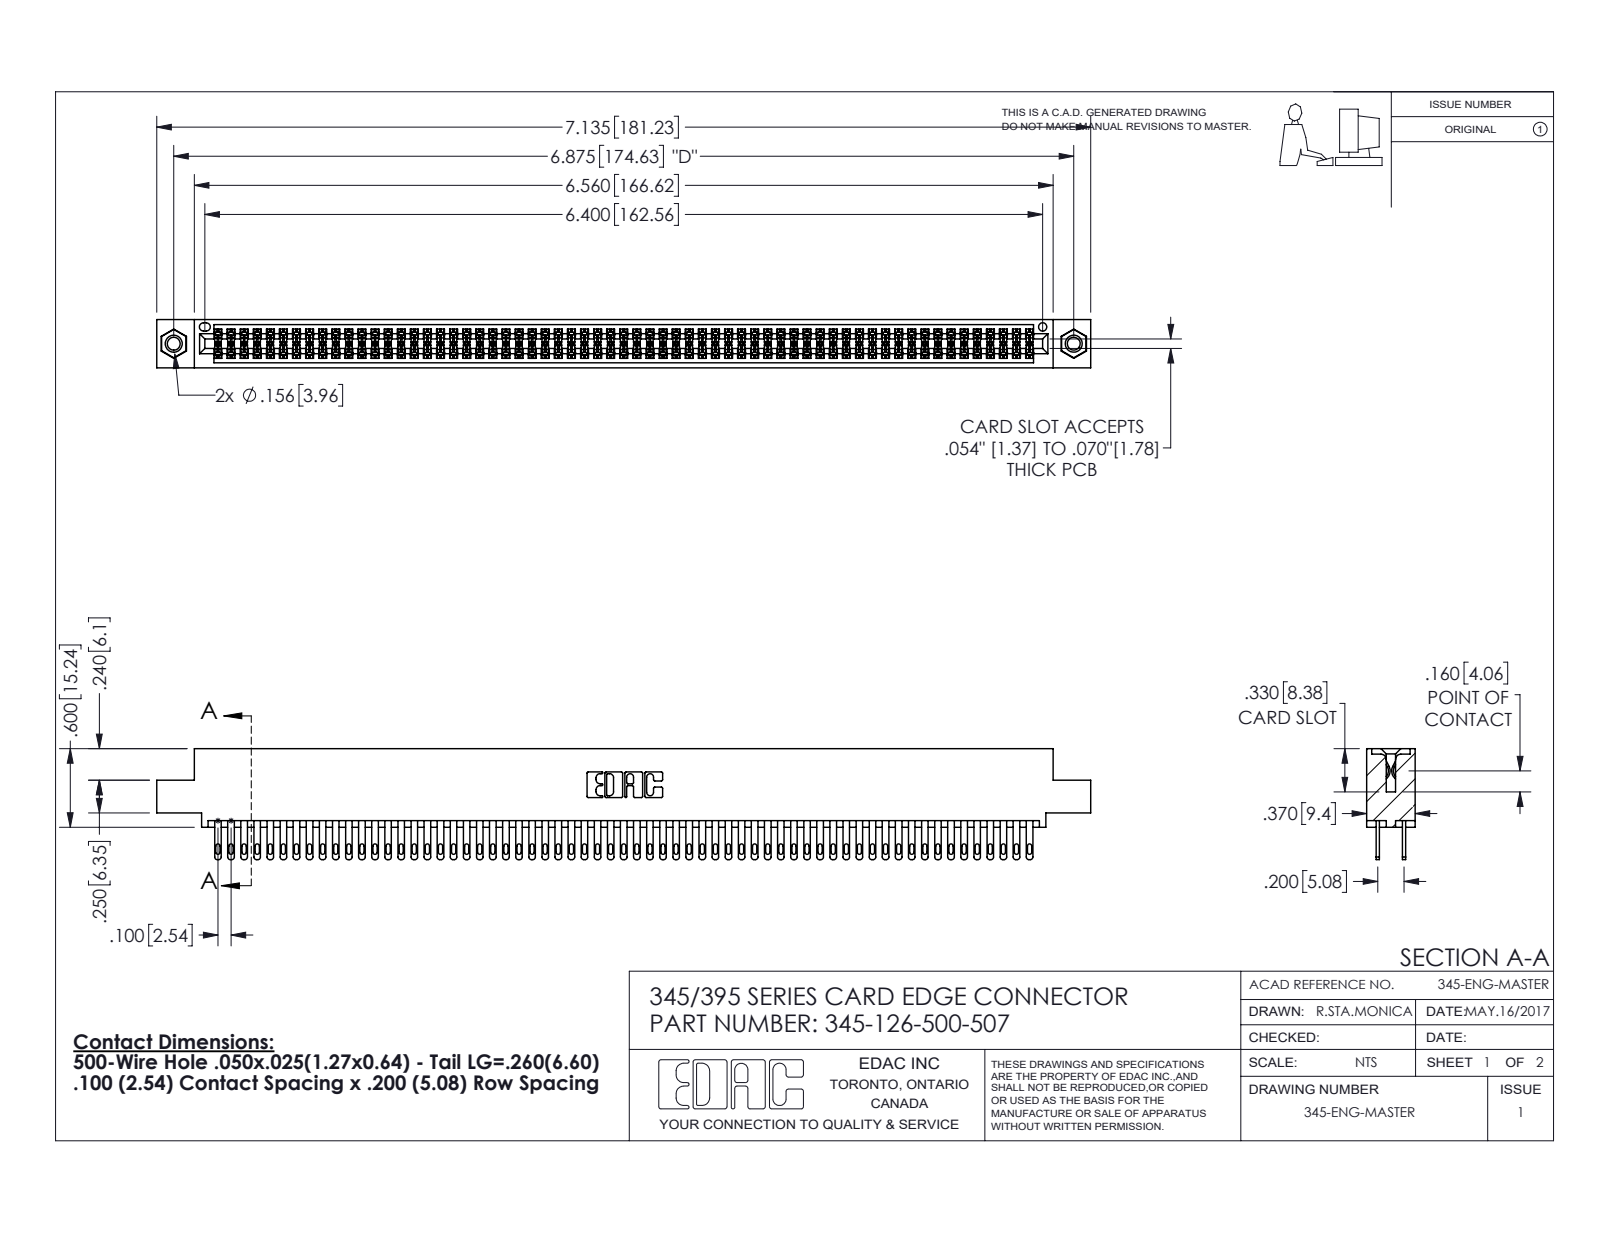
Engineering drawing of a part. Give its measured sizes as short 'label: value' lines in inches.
name: 345-250-001_345-250-005-103; 345-292-001_345-293-100; 345-126-500-507; 345 Part_0.110 Offset - 0.156 Dia-TI
written by: SolidWorks 2016 (CONFIG_CONTROL_DESIGN)
unit: in
bodies: 129 solids, 5986 faces (3518 planar, 2452 cylindrical, 16 other)
size: 7.135 × 0.847 × 0.37
volume: 1.104 in³; area: 44.27 in²
holes: 2× ⌀0.098, 2× ⌀0.125, 2× ⌀0.156, 1× ⌀0.064
bosses: 2× ⌀0.155
rounds: 189× R0.006, 126× R0.016, 126× R0.02, 22× R0.01, 6× R0.007, 6× R0.031, 3× R0.026, 2× R0.014
face distances: 0.072, 0.298, 0.2, 0.098, 0.272, 0.025, 0.37, 0.225, 0.175, 0.149
hole spacings: 0.27, 6.639, 6.875
